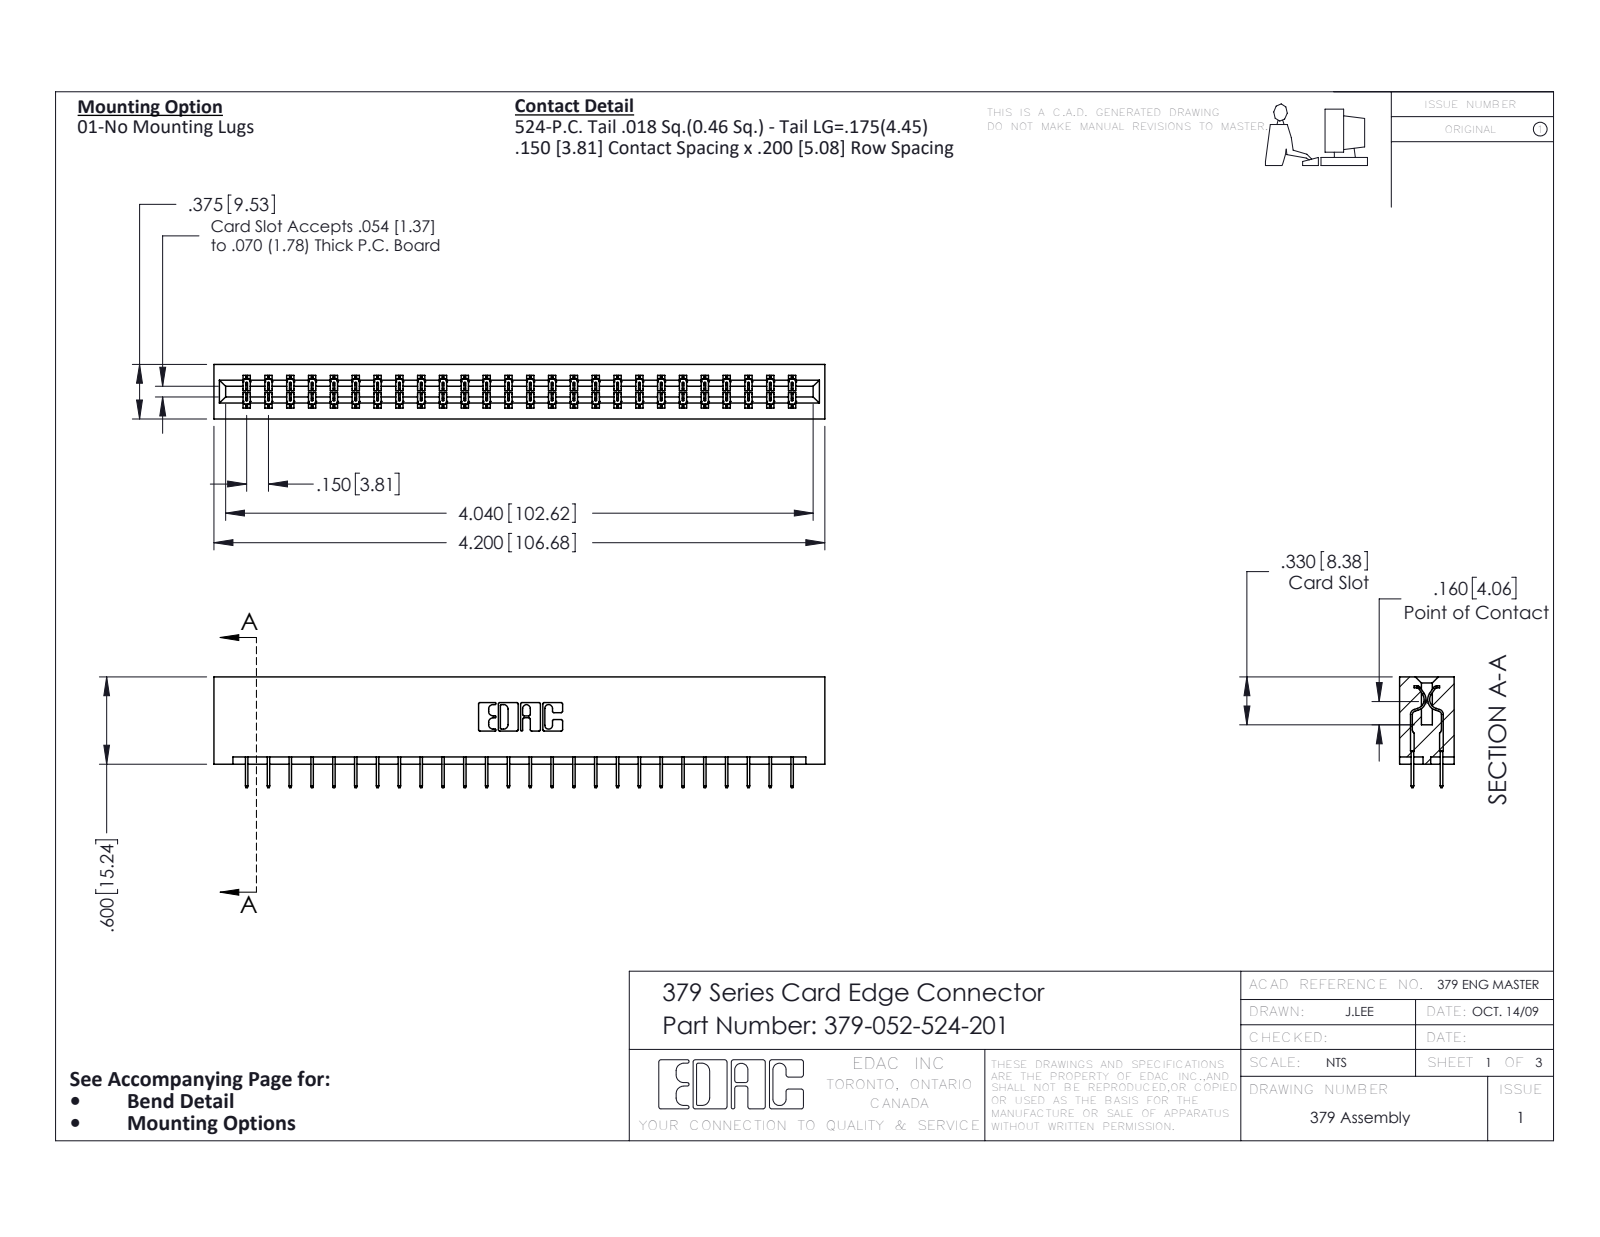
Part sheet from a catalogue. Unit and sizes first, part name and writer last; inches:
Units: inches
Overall size (bounding box): 4.2 × 0.762 × 0.375
Partial cylindrical surfaces — rounded edges, fillets, slot ends (radius × count): R0.006 ×78, R0.01 ×22, R0.007 ×6, R0.031 ×6, R0.026 ×3, R0.014 ×2, R0.022 ×2, R0.024 ×2
Main face-to-face distances: 0.3, 0.075, 0.375, 0.2, 0.225, 0.1, 0.55, 0.15, 0.15, 0.076
Volume: 0.722 in³ · Surface area: 20.05 in²
Bodies: 53 solids, 3018 faces (2250 planar, 768 cylindrical, 0 other)
Part name (STEP PRODUCT): 345-292-001_345-293-124; 379-052-524-201; 379 Part_Lugless
STEP written by: SolidWorks 2016 (CONFIG_CONTROL_DESIGN)
